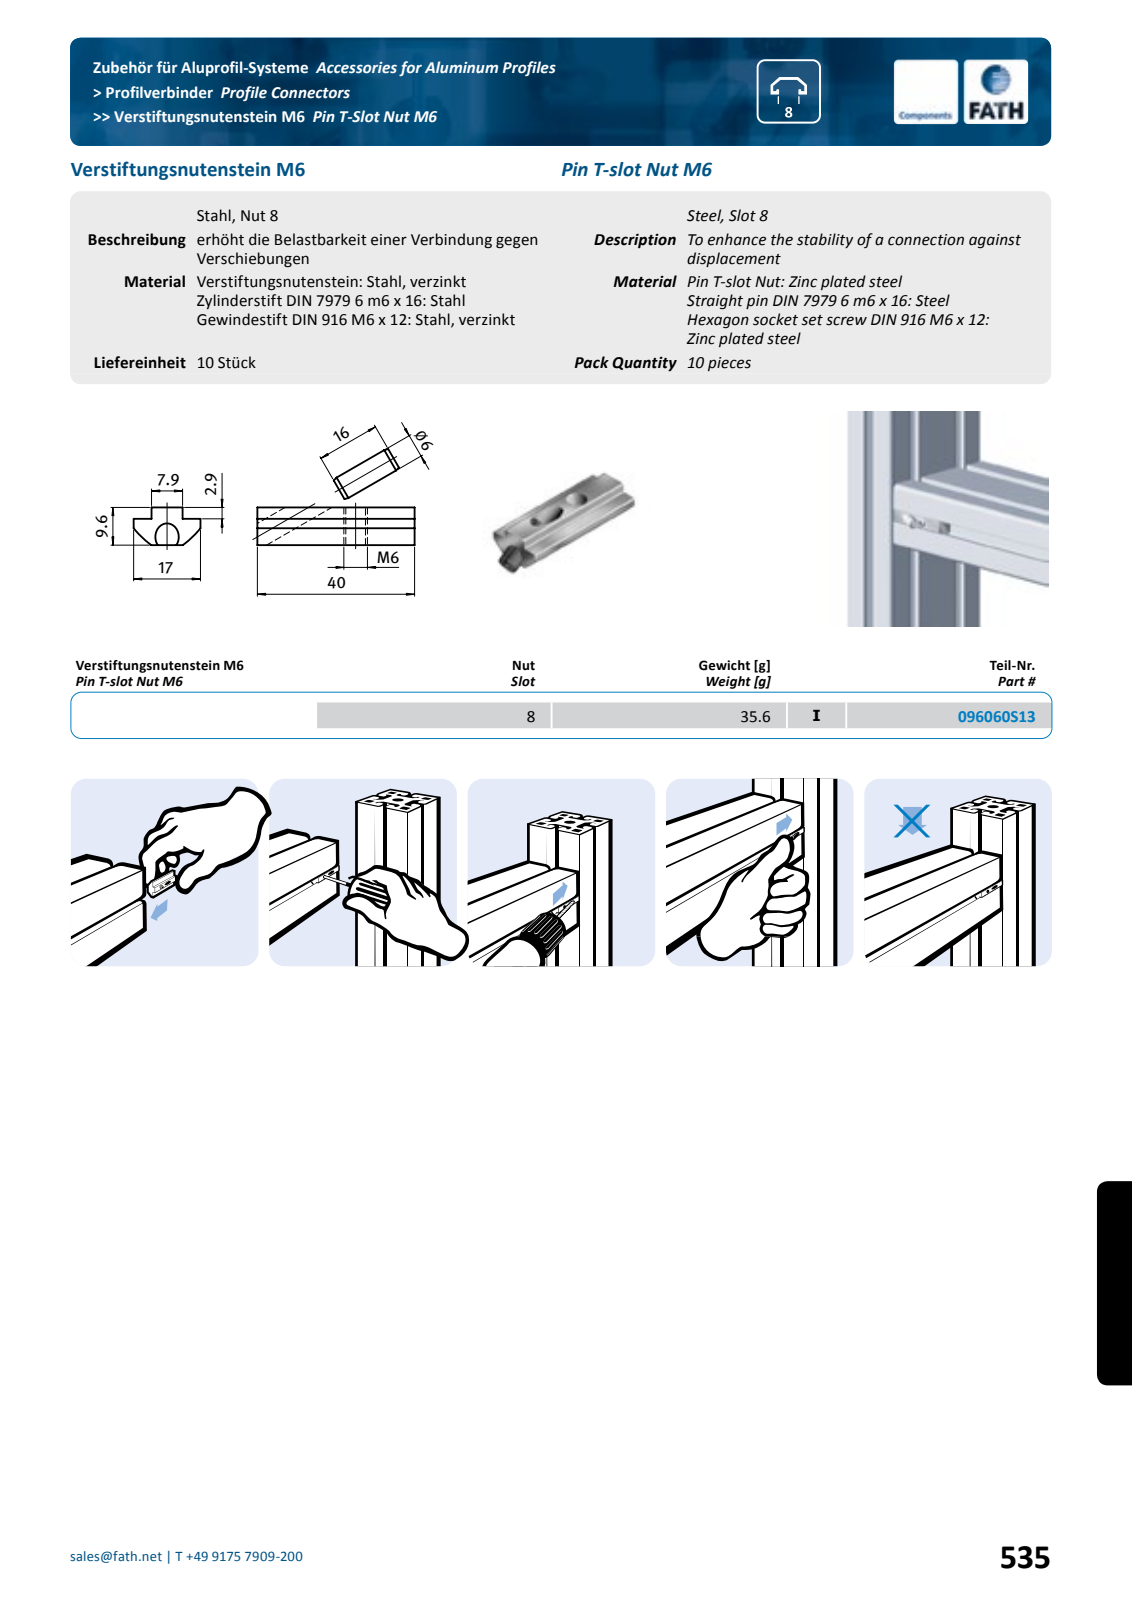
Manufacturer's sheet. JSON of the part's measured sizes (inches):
{"part_name": "fath_096060s13_1; fath_096060s13_2; fath_096060s13_3", "step_written_by": "Spatial InterOp 3D (automotive_design)", "units": "inches", "bodies": {"solids": 3, "faces": 47, "planar": 21, "cylindrical": 18, "other": 8}, "overall_size": [1.765, 0.669, 0.585], "volume_in3": 0.298, "surface_area_in2": 4.712, "round_holes": [[0.197, 1], [0.236, 1]], "round_bosses_or_shafts": [[0.236, 1]], "partial_cylinders_radius": [[0.02, 8], [0.965, 2]], "face_to_face_distances": [0.264, 0.378, 0.114, 0.179, 0.49, 1.575, 0.311, 0.669, 0.118, 0.63]}
